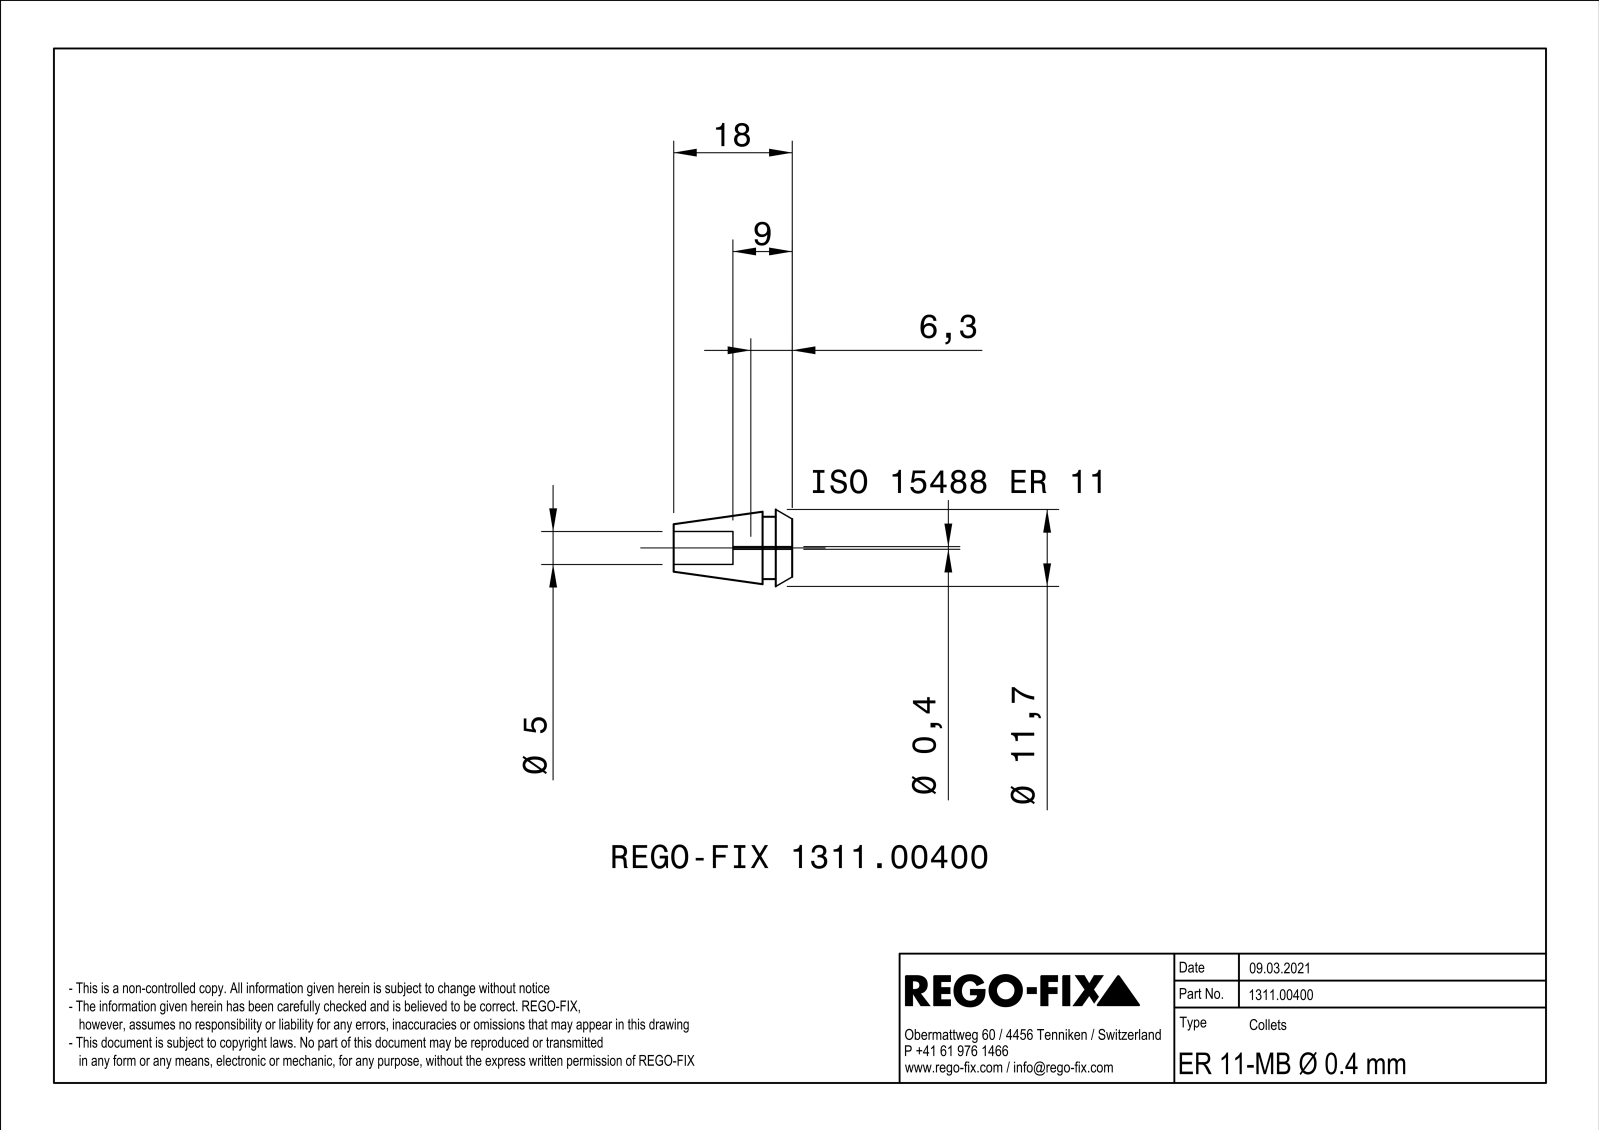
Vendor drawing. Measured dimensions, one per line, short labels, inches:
name: NOCUT
written by: SIEMENS PLM Software Solid Edge ST10 (AUTOMOTIVE_DESIGN)
unit: in
bodies: 1 solid, 91 faces (26 planar, 19 cylindrical, 46 other)
size: 0.709 × 0.439 × 0.438
volume: 0.055 in³; area: 1.869 in²
holes: 3× ⌀0.059, 1× ⌀0.197
bosses: 1× ⌀0.374
rounds: 3× R0.984, 1× R0.008
face distances: 0.031, 0.02, 0.177, 0.354, 0.098, 0.709, 0.61, 0.079, 0.531, 0.256
hole spacings: 0.067, 0.116
